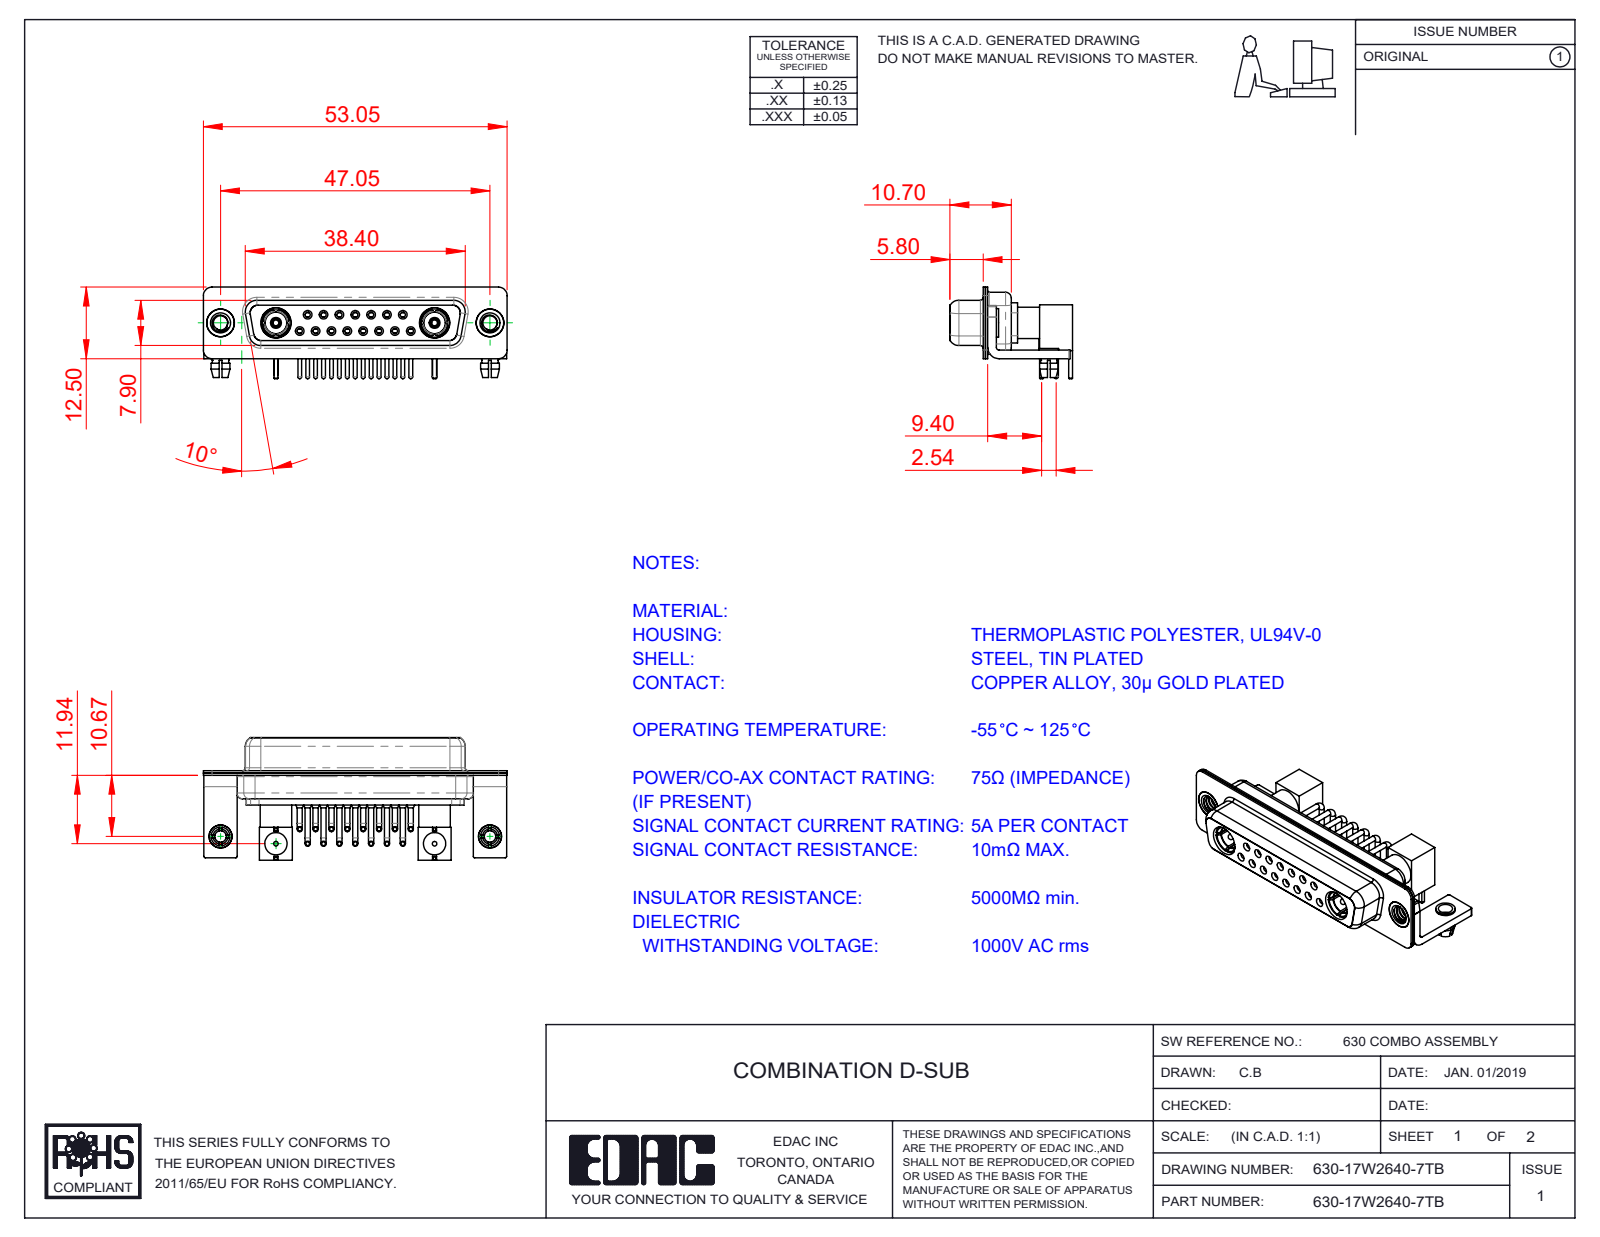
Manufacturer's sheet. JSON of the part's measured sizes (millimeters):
{"part_name": "Pin_RA; Locking Collar; 630-17W2640-7TB; 630Combo Contact Row 2 (+8 more)", "step_written_by": "SolidWorks 2020 (CONFIG_CONTROL_DESIGN)", "units": "millimeters", "bodies": {"solids": 36, "faces": 1540, "planar": 494, "cylindrical": 662, "other": 384}, "overall_size": [53.05, 21.41, 16], "volume_mm3": 4654, "surface_area_mm2": 11218, "round_holes": [[1.1, 17], [1.5, 17], [2, 17], [0.9, 15], [1.6, 8], [1.7, 7], [2.5, 4], [4.85, 4], [0.8, 2], [2.83, 2], [3.1, 2], [3.2, 2]], "round_bosses_or_shafts": [[0.9, 15], [0.65, 15], [1.6, 7], [5, 4], [4, 4], [2.9, 4], [0.8, 3], [5.5, 2]], "partial_cylinders_radius": [[0.25, 16], [1.5, 16], [2, 13], [1.35, 8], [1.6, 8], [0.5, 5], [0.6, 4], [0.65, 4]], "face_to_face_distances": [0.4, 1.4, 0.45, 1.8, 8.45, 0.8, 8.9, 6.2, 7.05, 1.35], "hole_center_spacings": [3.16, 2.77, 5.54, 8.31, 5.04, 7.49, 11.08, 5.03]}
